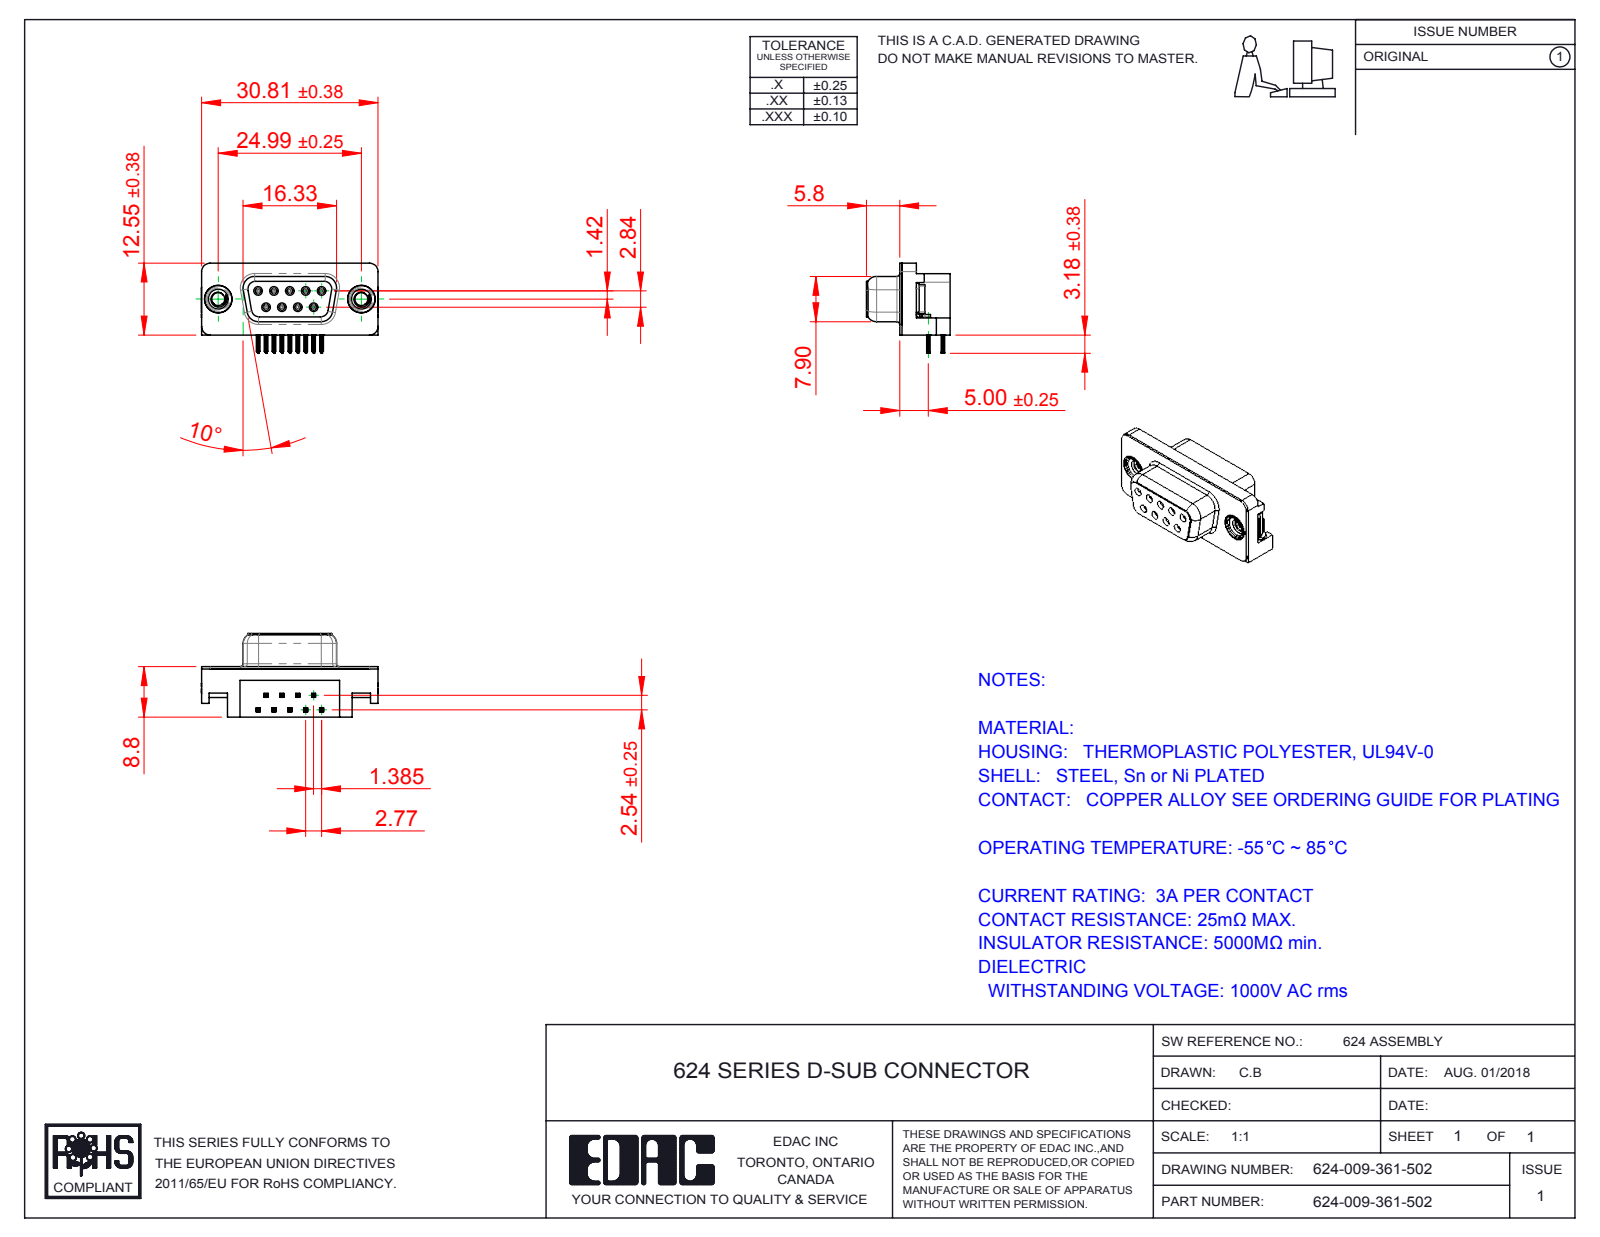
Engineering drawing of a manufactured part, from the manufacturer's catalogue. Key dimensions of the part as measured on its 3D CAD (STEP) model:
Part name (STEP PRODUCT): 624 Contact Top; 624-009-361-502; 624 Socket Bottom; 624 Non Board Mount (+3 more)
STEP written by: SolidWorks 2016 (CONFIG_CONTROL_DESIGN)
Units: millimetres
Bodies: 15 solids, 1520 faces (642 planar, 406 cylindrical, 472 other)
Overall size (bounding box): 30.89 × 15.73 × 14.6
Volume: 2 938 mm³ · Surface area: 4 335 mm²
Round holes (diameter × count): ⌀0.8 ×9, ⌀0.9 ×9, ⌀2.26 ×2, ⌀4 ×2, ⌀4.8 ×2, ⌀5 ×2
Round bosses / shafts (diameter × count): ⌀1.2 ×9, ⌀4.9 ×2, ⌀4.75 ×2, ⌀3.9 ×2
Partial cylindrical surfaces — rounded edges, fillets, slot ends (radius × count): R0.1 ×72, R0.15 ×36, R0.35 ×18, R1 ×18, R0.34 ×9, R0.25 ×8, R1.35 ×8, R1.5 ×7
Main face-to-face distances: 0.4, 8.4, 8.8, 2.9, 2.5, 6.2, 5.9, 0.35, 10.69, 10.34
Hole centre spacings: 3.16, 2.77, 5.54, 5.03, 5.04, 8.31, 7.48, 7.49
